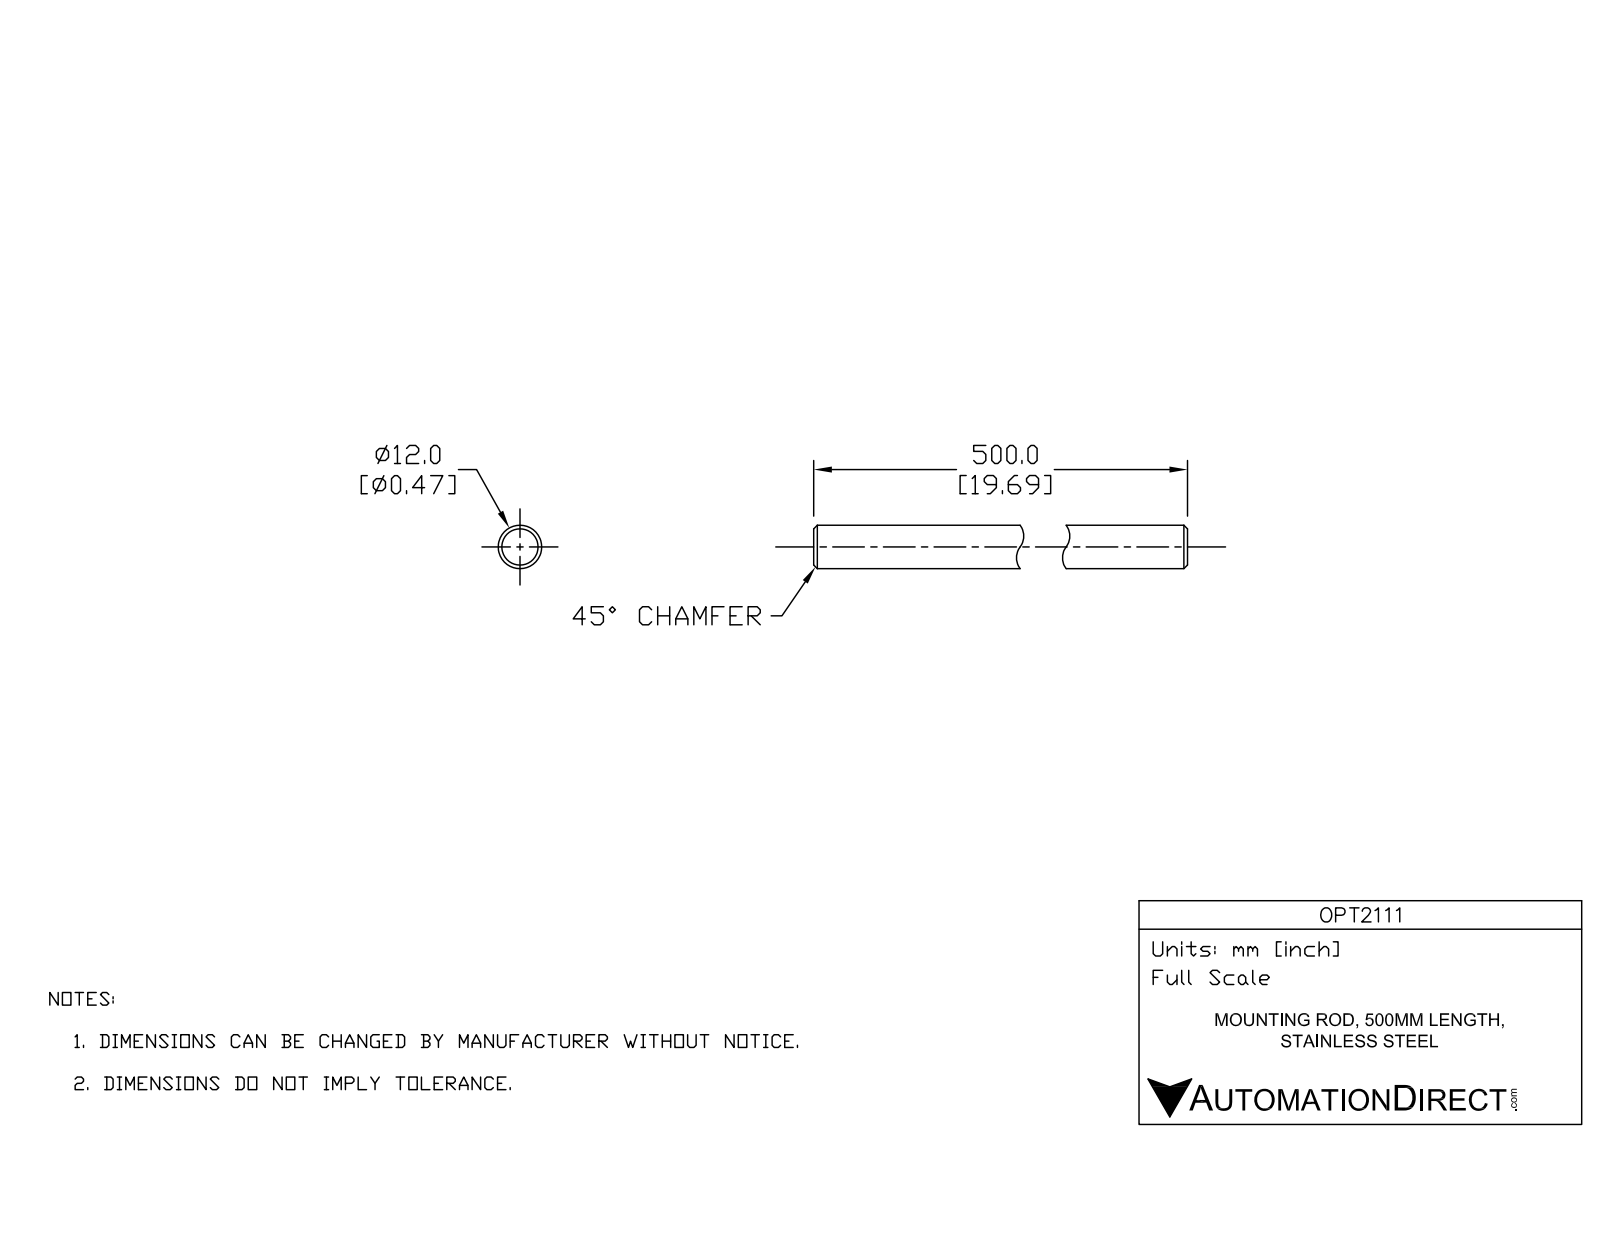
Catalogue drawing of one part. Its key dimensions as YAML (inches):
step_written_by: "Unknown (CONFIG_CONTROL_DESIGN)"
units: inches
bodies: {solids: 1, faces: 5, planar: 2, cylindrical: 1, other: 2}
overall_size: [19.685, 0.472, 0.472]
volume: 3.449
surface_area: 29.5
round_bosses_or_shafts:
  - {diameter: 0.472, count: 1}
face_to_face_distances: [19.685]
